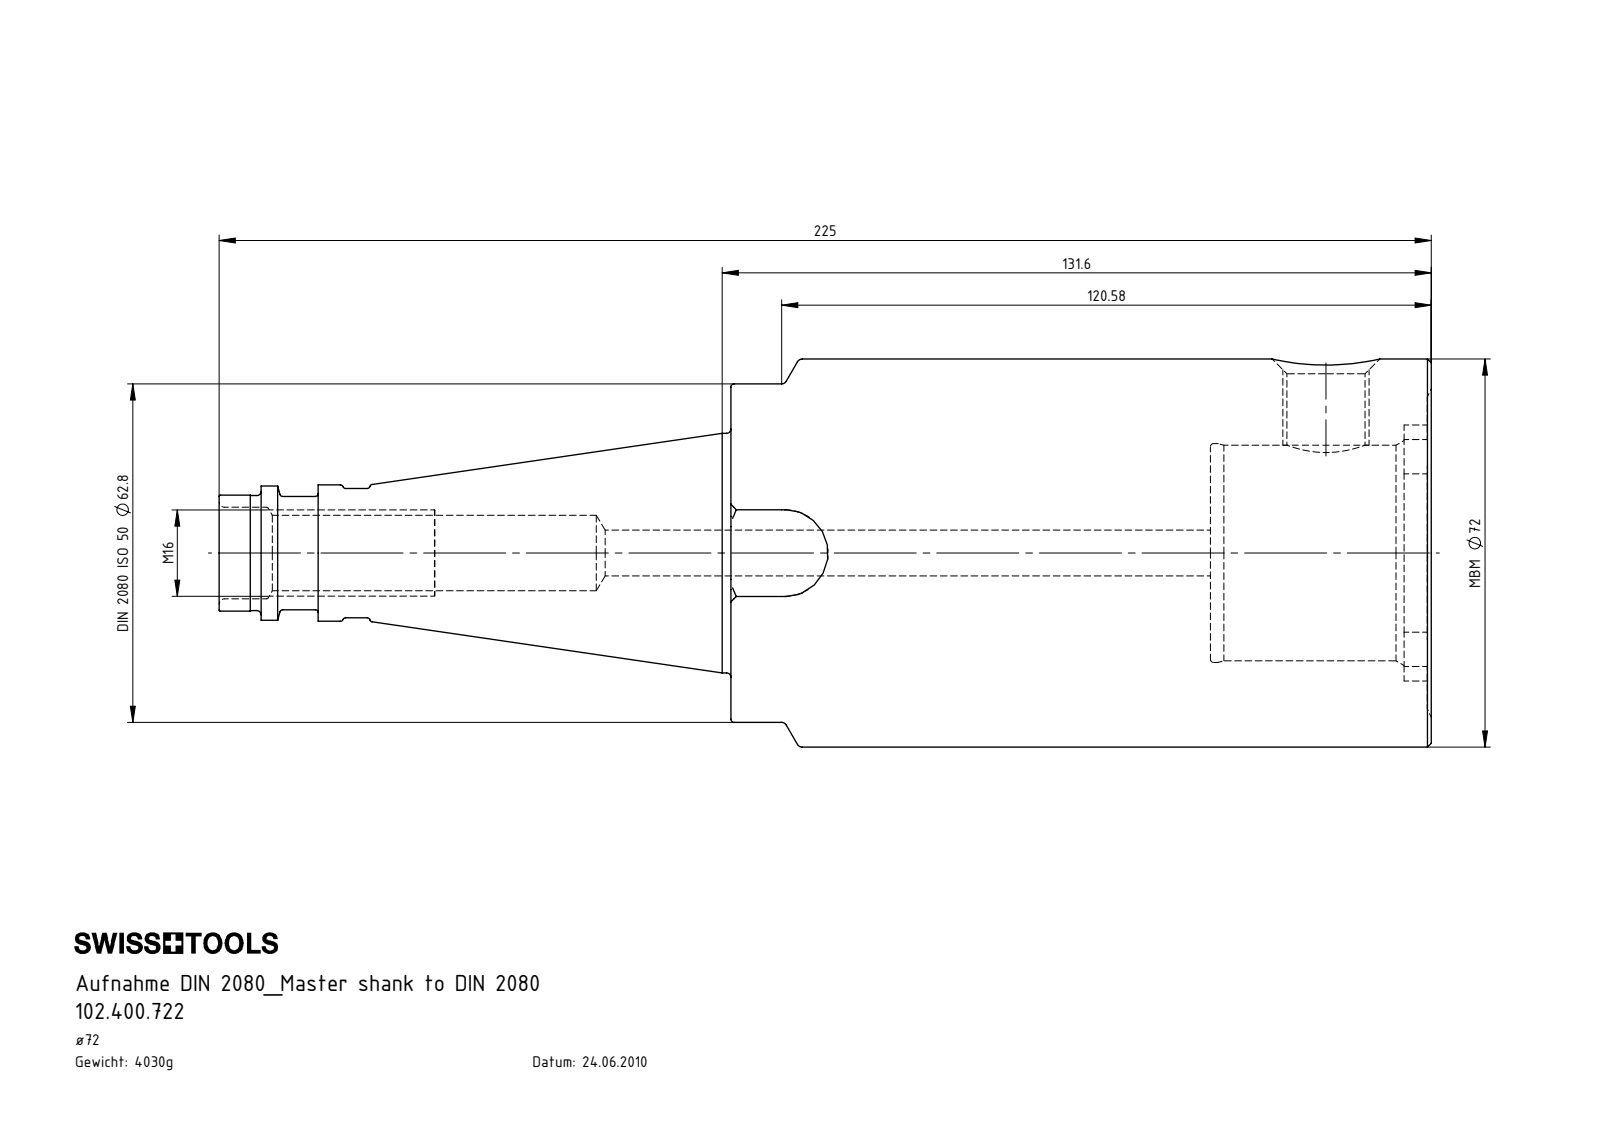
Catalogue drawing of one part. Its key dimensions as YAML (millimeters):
part_name: "102.400.722"
step_written_by: "SolidWorks 2017 (CONFIG_CONTROL_DESIGN)"
units: millimeters
bodies: {solids: 1, faces: 137, planar: 28, cylindrical: 52, other: 57}
overall_size: [225, 72, 72]
volume: 513339
surface_area: 57398
round_holes:
  - {diameter: 8.5, count: 1}
  - {diameter: 14, count: 1}
  - {diameter: 14.5, count: 1}
  - {diameter: 17, count: 1}
  - {diameter: 40, count: 1}
  - {diameter: 40.6, count: 1}
round_bosses_or_shafts:
  - {diameter: 72, count: 1}
  - {diameter: 62.8, count: 1}
  - {diameter: 44.45, count: 1}
  - {diameter: 25.3, count: 1}
  - {diameter: 24.91, count: 1}
  - {diameter: 24, count: 1}
  - {diameter: 21.5, count: 1}
  - {diameter: 21.35, count: 1}
partial_cylinders:
  - {radius: 1.6, count: 8}
  - {radius: 5.2, count: 4}
  - {radius: 8.05, count: 1}
  - {radius: 23.75, count: 1}
  - {radius: 28.02, count: 1}
face_to_face_distances: [89, 130, 41, 124.95, 35.95, 5.05, 129.25, 40.25, 4.3, 0.75]
